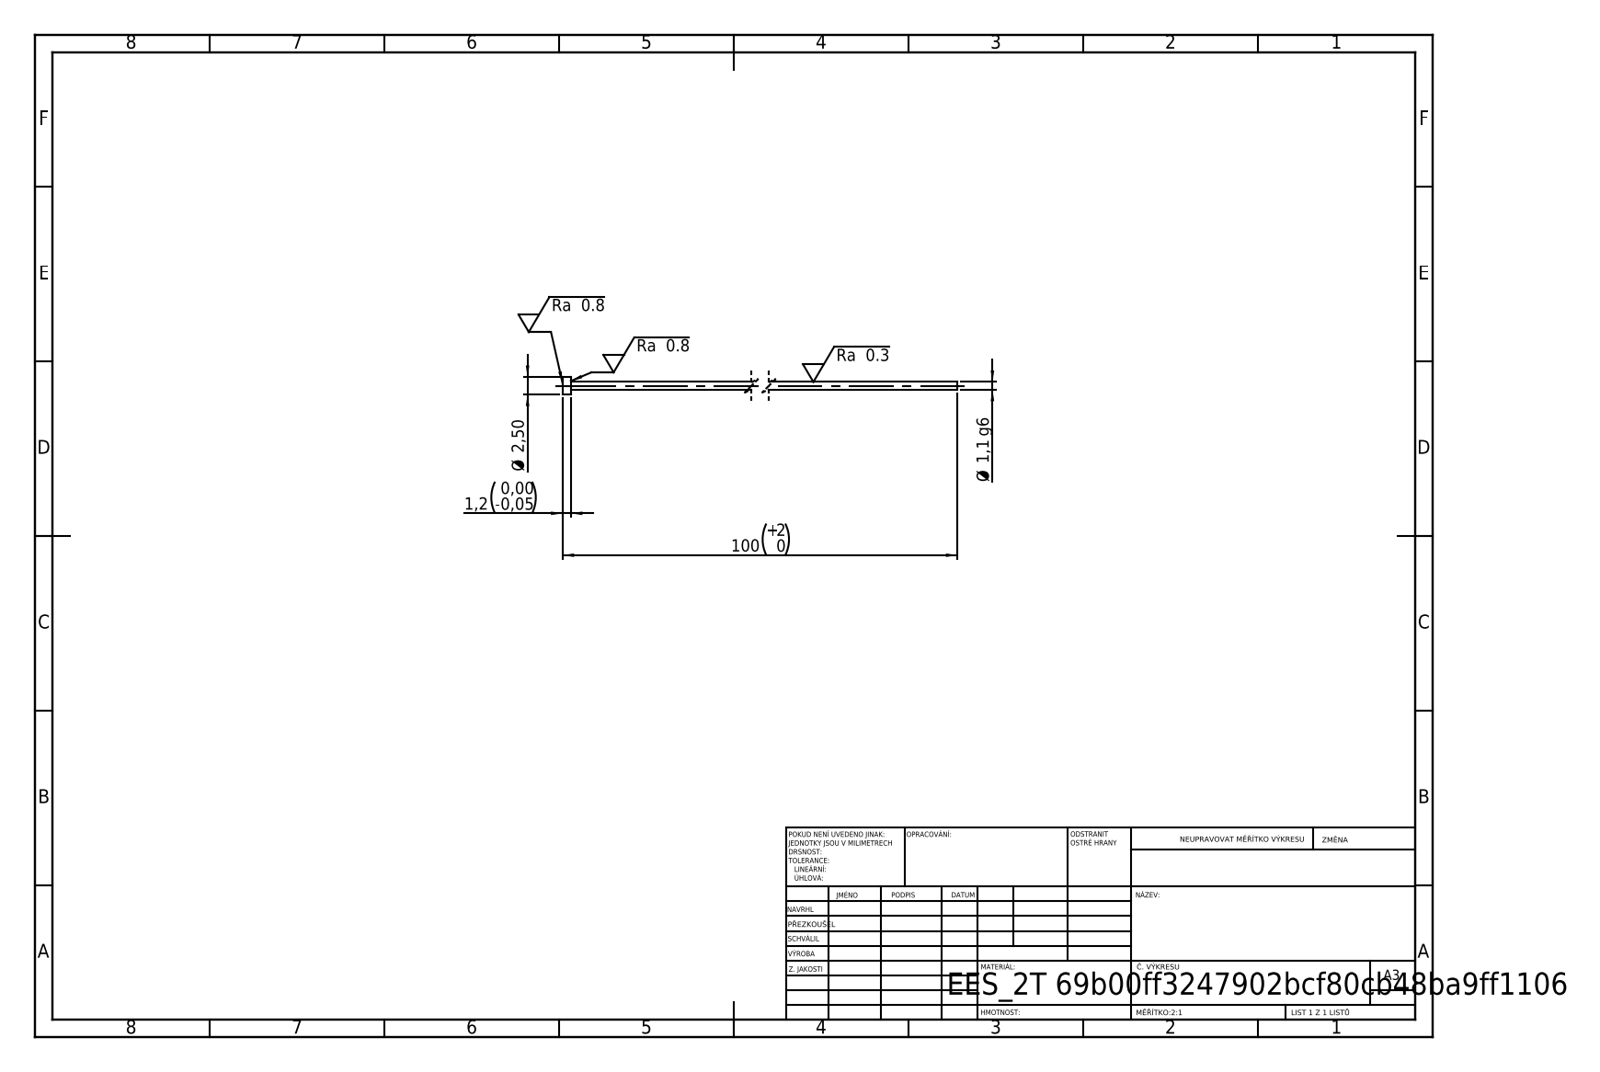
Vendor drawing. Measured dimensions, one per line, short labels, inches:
written by: SolidWorks 2019 (CONFIG_CONTROL_DESIGN)
unit: in
bodies: 1 solid, 7 faces (3 planar, 4 cylindrical, 0 other)
size: 3.937 × 0.098 × 0.098
volume: 0.006 in³; area: 0.56 in²
bosses: 1× ⌀0.098, 1× ⌀0.043
face distances: 0.047, 3.937, 3.89
